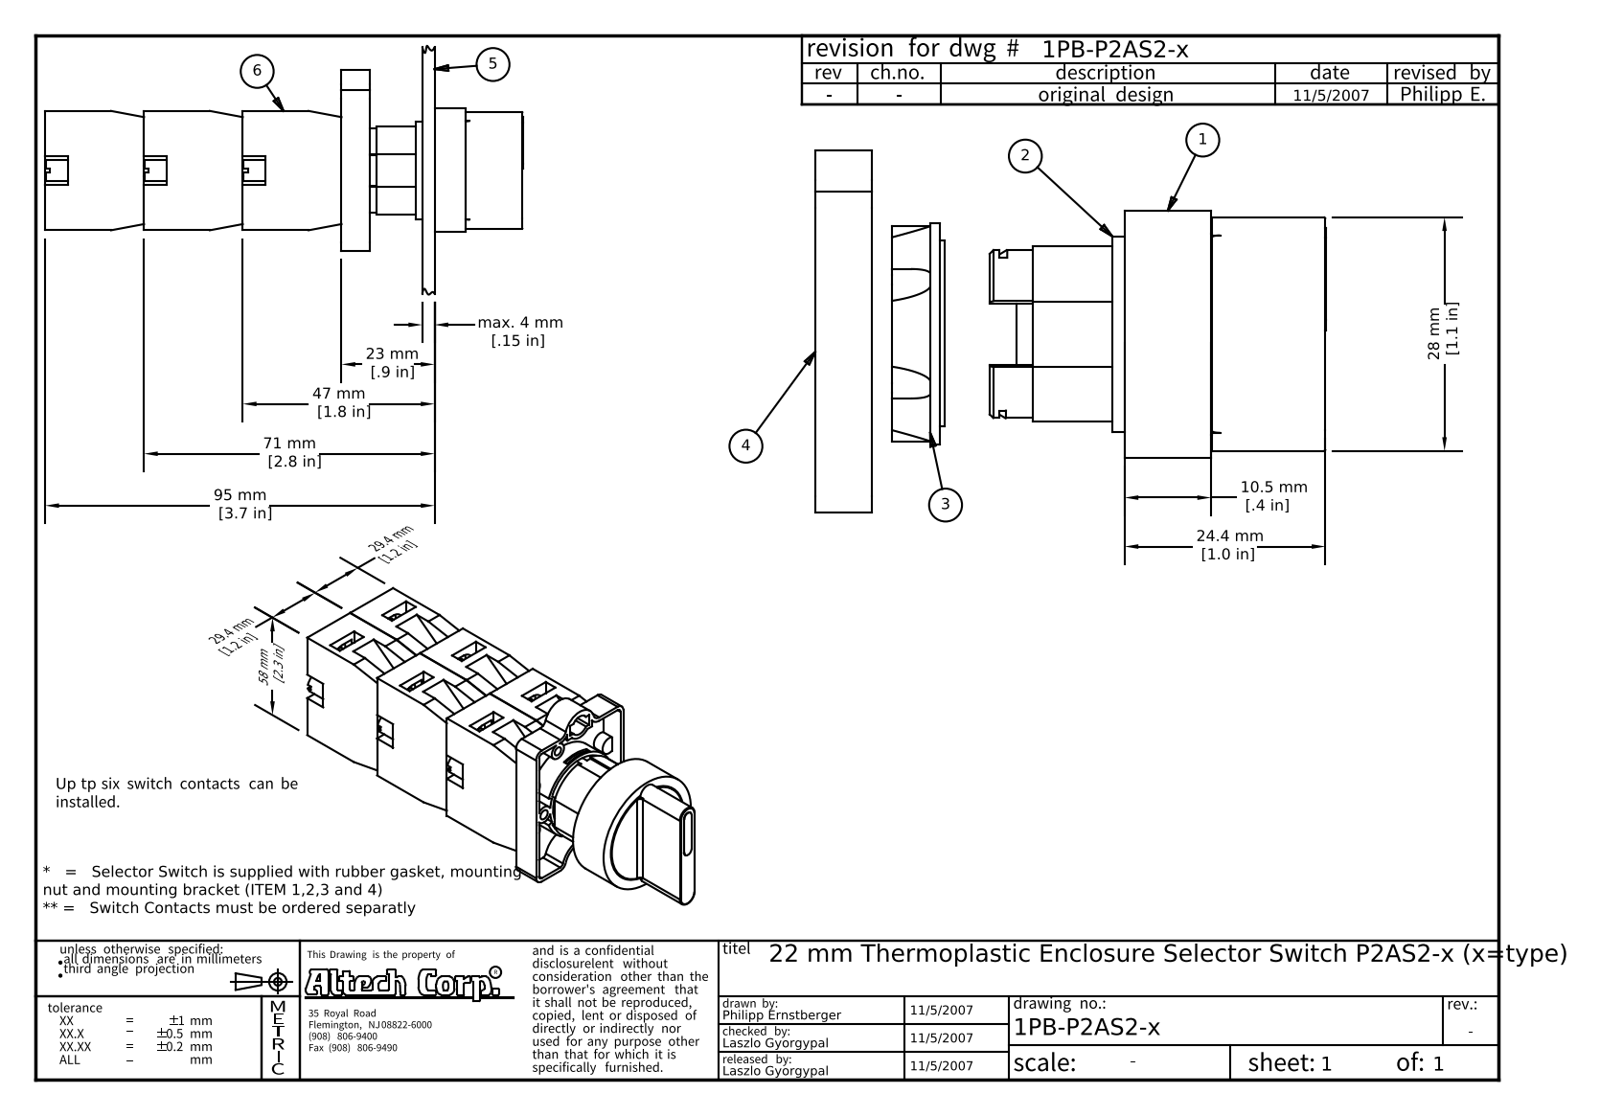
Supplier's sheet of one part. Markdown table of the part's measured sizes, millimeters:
| quantity | value |
| --- | --- |
| part name | P2AS2-x_assembly; P2AS2-x_operator; P2AS2-x; 2PRG1 (+7 more) |
| STEP written by | Autodesk Inventor 2008 (AUTOMOTIVE_DESIGN) |
| units | millimeters |
| bodies | 30 solids, 1209 faces (648 planar, 219 cylindrical, 342 other) |
| overall size | 116.1 × 60.45 × 45 |
| volume | 76 853 mm³ |
| surface area | 47 238 mm² |
| round holes (diameter × count) | 2.5 × 6, 2.2 × 2, 2.6 × 2, 17.6 × 1, 20.8 × 1, 22.5 × 1, 25 × 1 |
| round bosses / shafts (diameter × count) | 3 × 6, 2.75 × 4, 1.5 × 4, 5 × 2, 4.2 × 2, 30 × 1, 26.8 × 1, 24.5 × 1 |
| partial cylindrical surfaces (radius × count) | 1.5 × 24, 1 × 17, 2 × 8, 2.25 × 6, 0.2 × 2, 1.25 × 2, 2.5 × 2, 3 × 2 |
| main face-to-face distances | 14.8, 14.7, 24, 3, 48, 29.5, 22.6, 29, 19.6, 67.6 |
| hole center spacings | 6.54, 26.07, 11.41, 12.25, 13, 14.51, 14.56, 17.17 |
